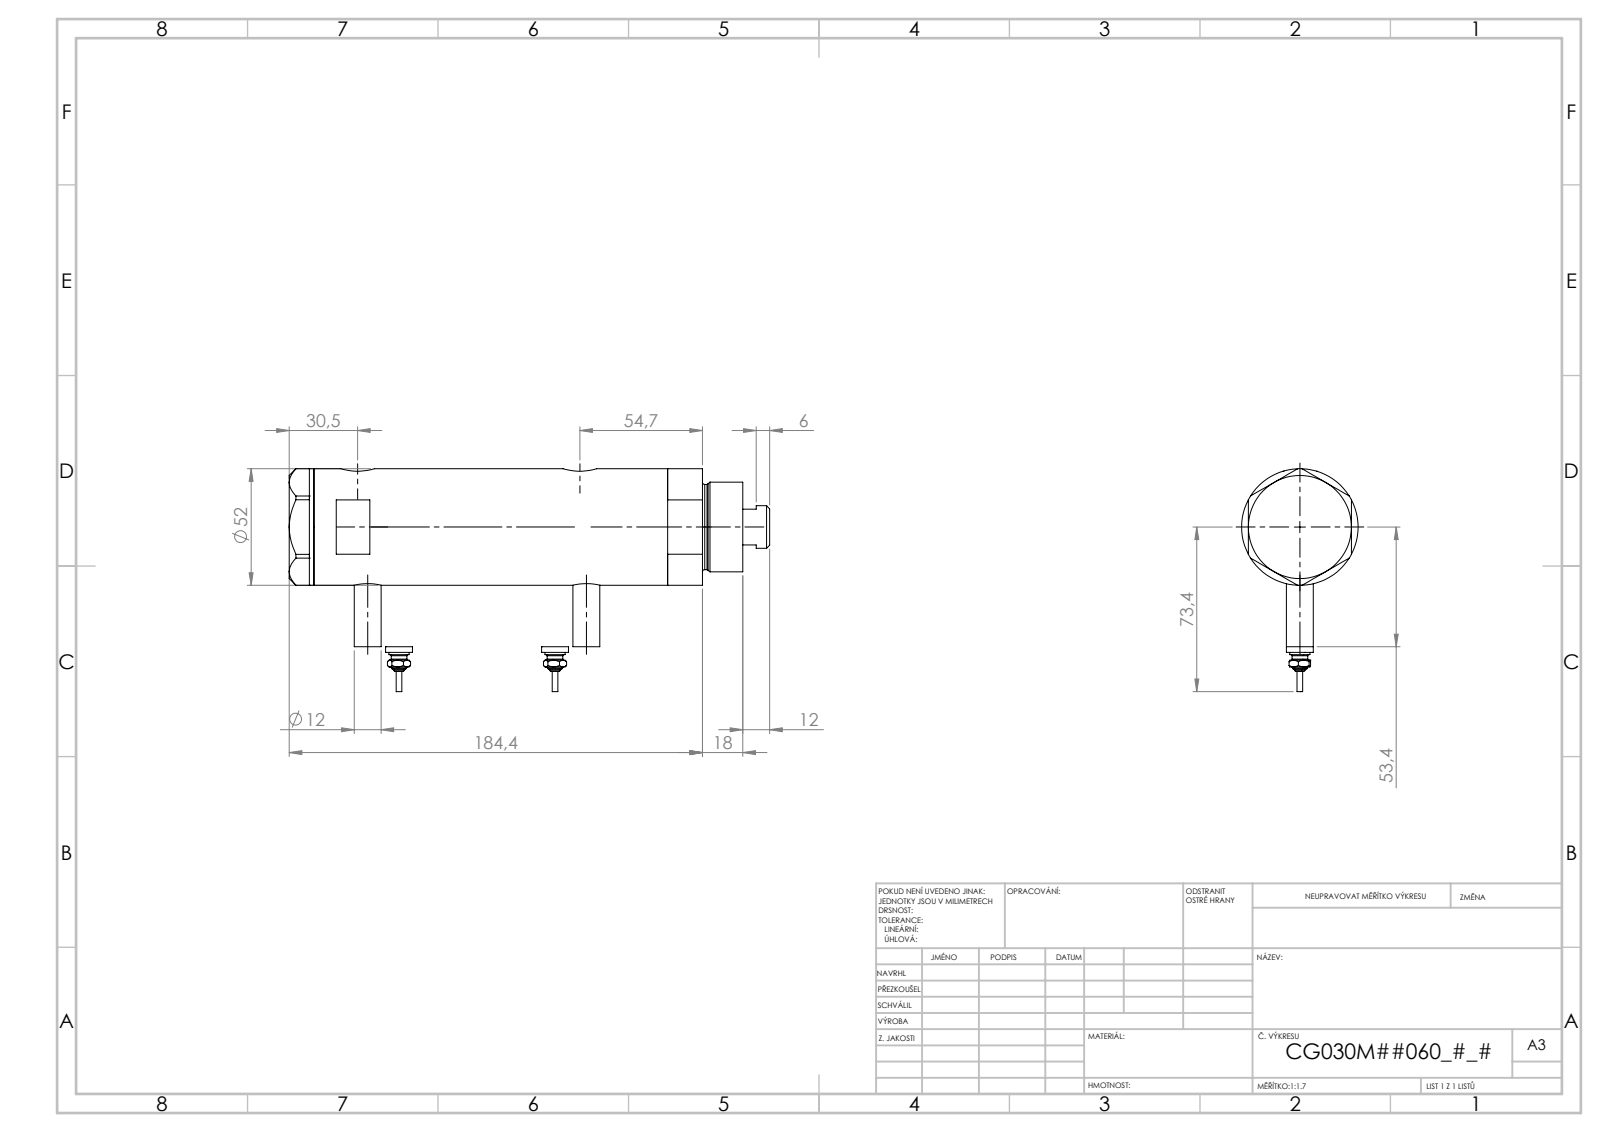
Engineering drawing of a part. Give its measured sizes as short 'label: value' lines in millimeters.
name: V270CG_MIDDLE; V270CG_BACK; V270CG_VC; V270CG_FRONT (+1 more)
written by: SolidWorks 2019 (CONFIG_CONTROL_DESIGN)
unit: mm
bodies: 6 solids, 246 faces (95 planar, 77 cylindrical, 74 other)
size: 209.02 × 84.3 × 52
volume: 374 236 mm³; area: 86 263 mm²
holes: 2× ⌀5, 2× ⌀9.73, 2× ⌀12.5, 2× ⌀15, 1× ⌀6.5, 1× ⌀20, 1× ⌀21.5, 1× ⌀30, 1× ⌀33, 1× ⌀44
bosses: 3× ⌀12, 2× ⌀9, 2× ⌀7, 2× ⌀4.34, 2× ⌀2.4, 1× ⌀52, 1× ⌀40, 1× ⌀38
face distances: 23.8, 124.55, 46, 11, 11.01, 113.55, 113.54, 160.95, 149.95, 149.94
hole spacings: 2.9, 4.5, 86.75, 89.65, 91.25, 94.15, 2.89, 2.91
